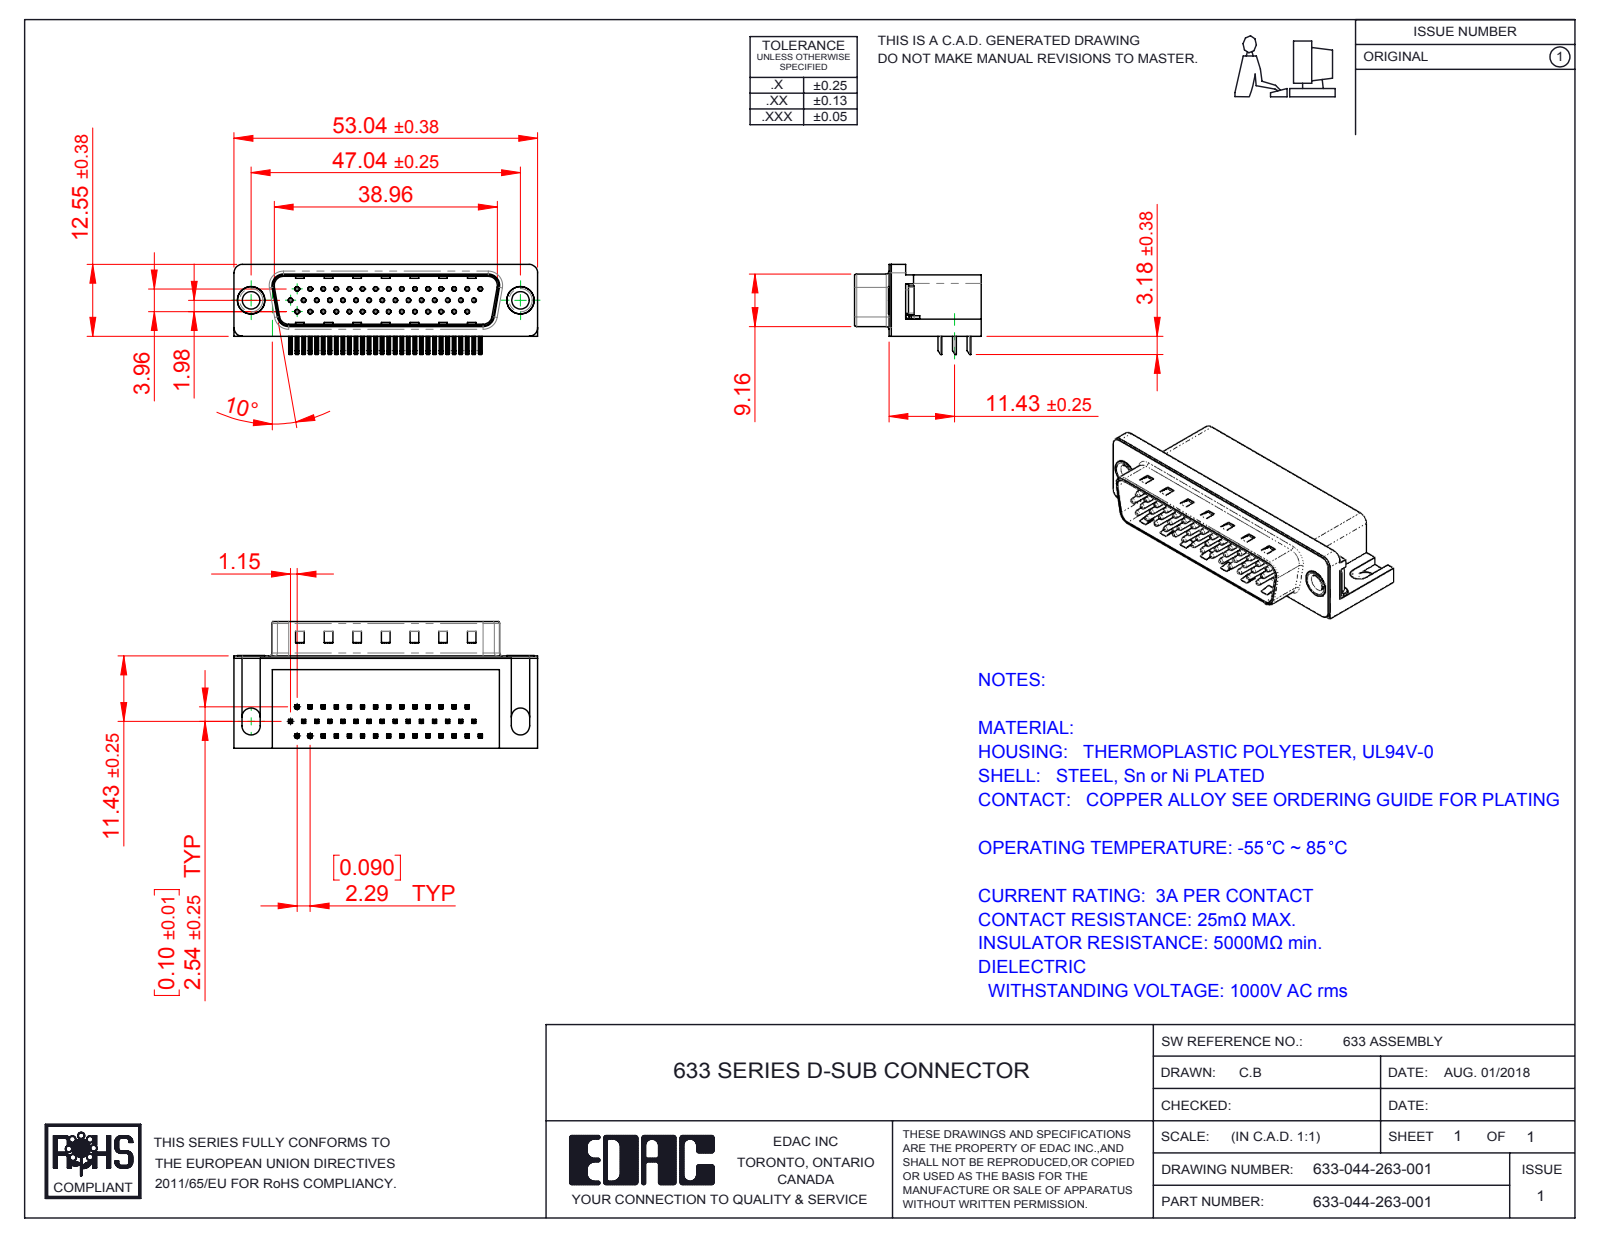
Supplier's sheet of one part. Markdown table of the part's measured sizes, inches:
| quantity | value |
| --- | --- |
| part name | 633 Contact Top; 633 Thru Hole Rivet; 633 Contact Bottom; 633 Contact Middle (+4 more) |
| STEP written by | SolidWorks 2016 (CONFIG_CONTROL_DESIGN) |
| units | inches |
| bodies | 50 solids, 3646 faces (2317 planar, 1038 cylindrical, 291 other) |
| overall size | 2.088 × 0.87 × 0.619 |
| volume | 0.492 in³ |
| surface area | 15.46 in² |
| round holes (diameter × count) | 0.014 × 44, 0.031 × 44, 0.12 × 2, 0.157 × 2, 0.189 × 2, 0.197 × 2 |
| round bosses / shafts (diameter × count) | 0.03 × 44, 0.193 × 2, 0.187 × 2, 0.152 × 2 |
| partial cylindrical surfaces (radius × count) | 0.01 × 184, 0.005 × 88, 0.039 × 16, 0.02 × 9, 0.063 × 8, 0.059 × 7, 0.035 × 4, 0.079 × 4 |
| main face-to-face distances | 0.016, 0.407, 0.618, 0.345, 0.114, 0.098, 0.083, 0.634, 0.421, 0.1 |
| hole center spacings | 0.09, 0.18, 0.18, 0.09, 0.27, 0.361, 0.451, 0.089 |
